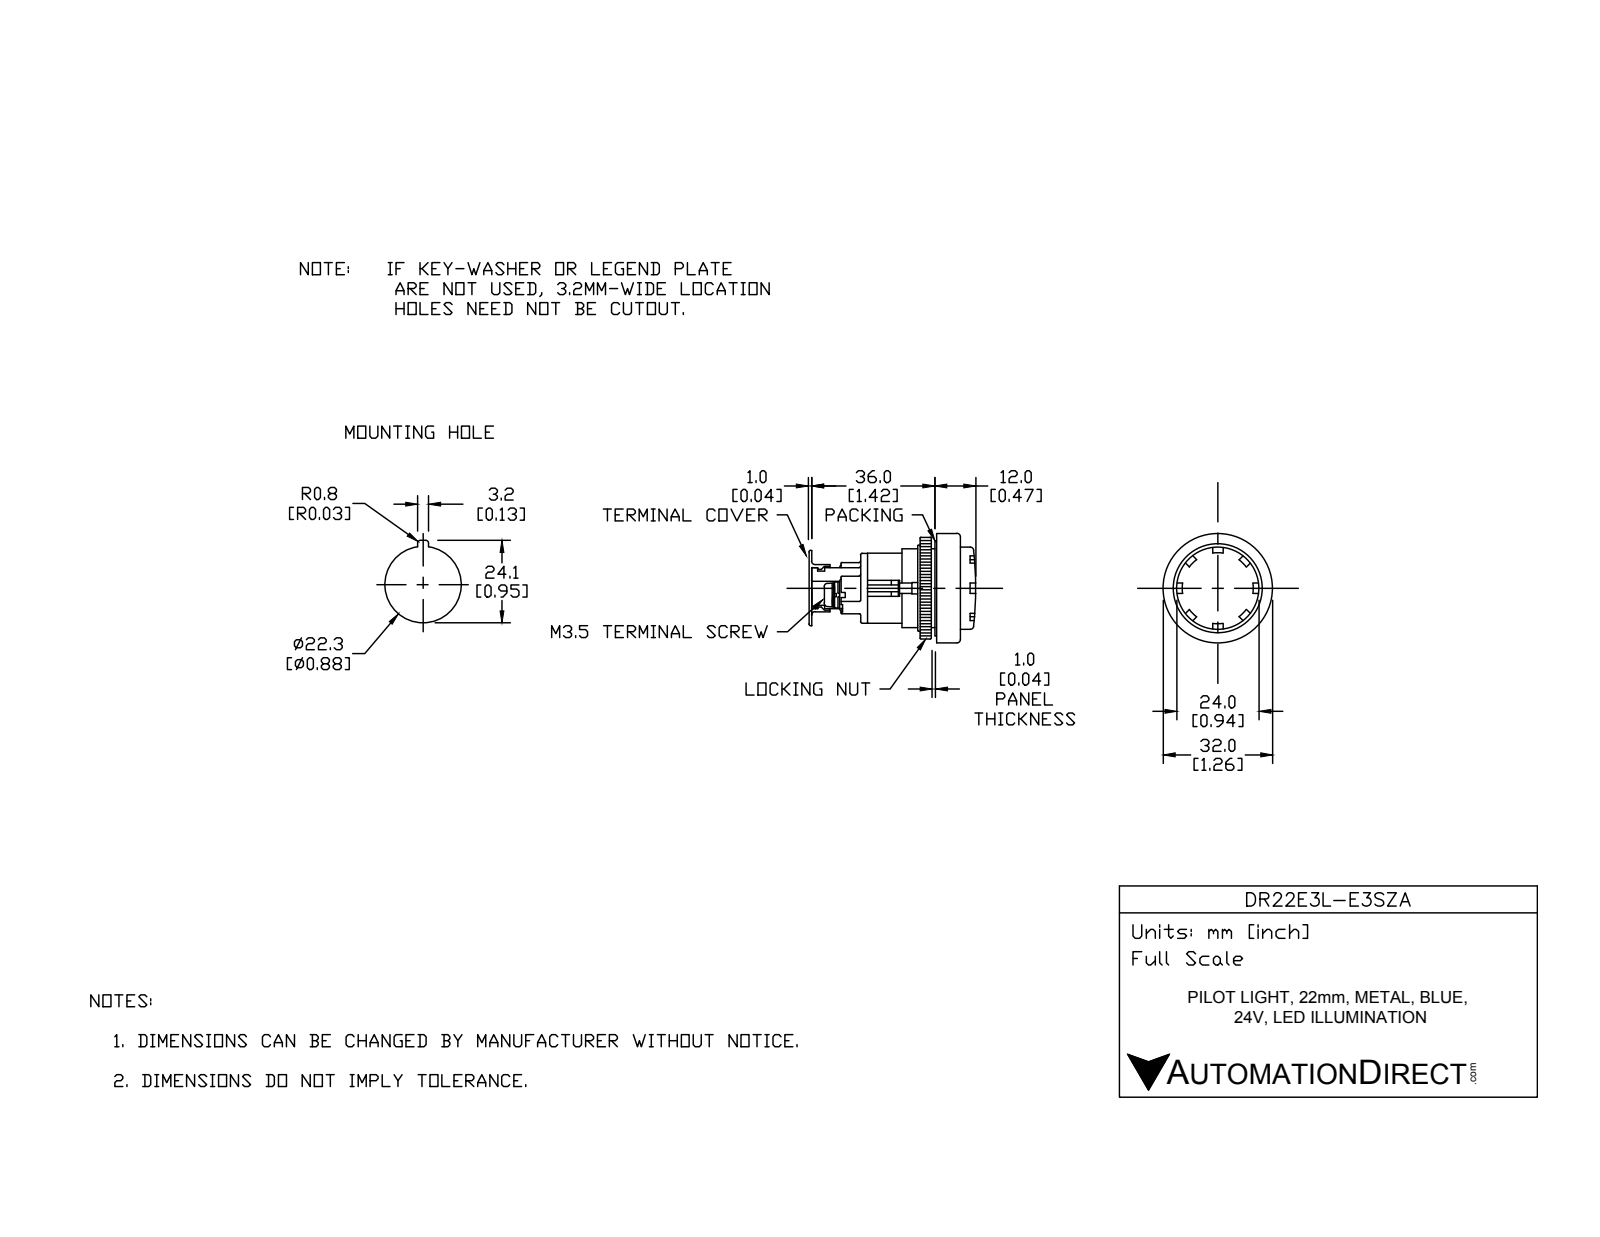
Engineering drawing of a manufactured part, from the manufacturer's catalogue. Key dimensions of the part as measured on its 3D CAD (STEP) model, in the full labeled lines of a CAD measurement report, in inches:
Part name (STEP PRODUCT): DR22E3L-E3SZA
STEP written by: SolidWorks 2017 (AUTOMOTIVE_DESIGN)
Units: inches
Bodies: 11 solids, 126 faces (76 planar, 38 cylindrical, 12 other)
Overall size (bounding box): 1.89 × 1.26 × 1.26
Volume: 1.188 in³ · Surface area: 17.73 in²
Round holes (diameter × count): ⌀0.252 ×2, ⌀0.866 ×1, ⌀0.984 ×1, ⌀1.181 ×1
Round bosses / shafts (diameter × count): ⌀0.228 ×2, ⌀1.26 ×1, ⌀1.169 ×1, ⌀1.161 ×1, ⌀1.063 ×1, ⌀0.858 ×1
Partial cylindrical surfaces — rounded edges, fillets, slot ends (radius × count): R0.02 ×8
Main face-to-face distances: 0.157, 1.024, 0.236, 0.63, 0.039, 0.787, 1.063, 1.654, 0.591, 0.433
Hole centre spacings: 0.238, 0.476
